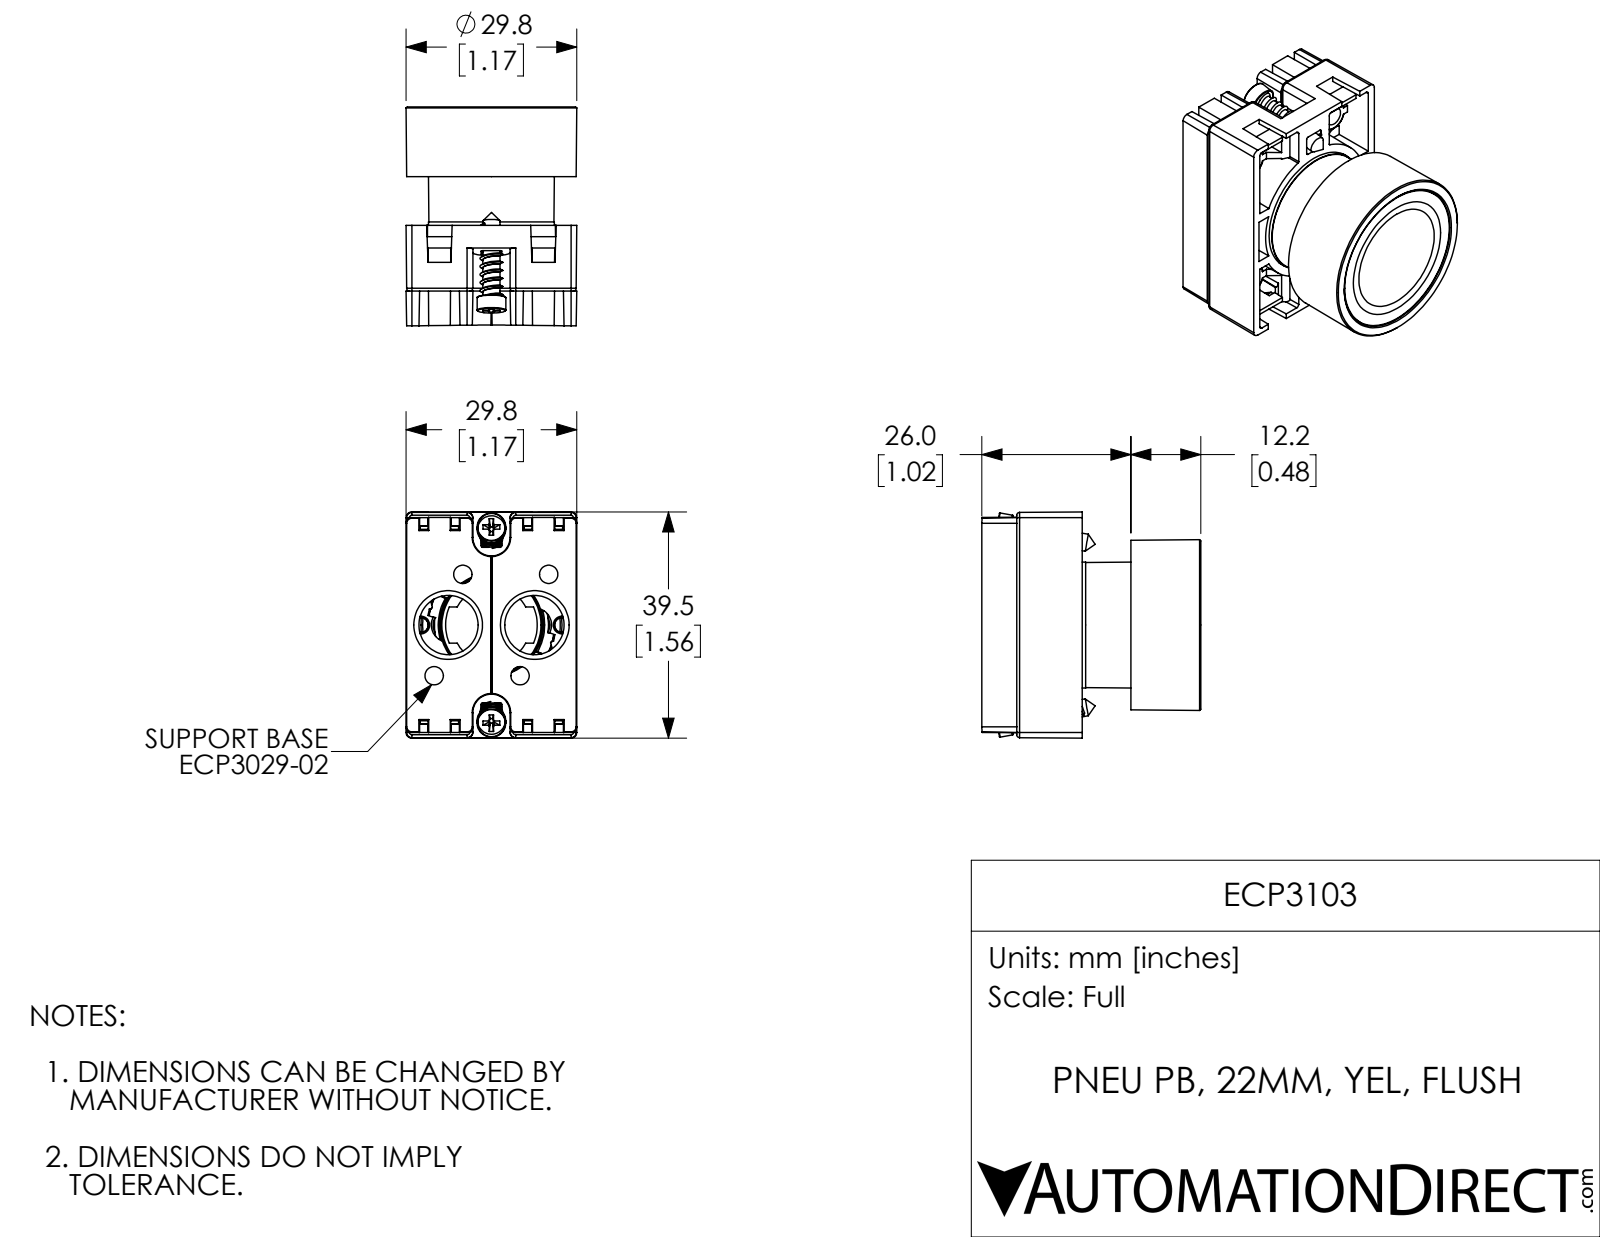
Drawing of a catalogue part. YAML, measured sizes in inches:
part_name: "ECP3103"
step_written_by: "SolidWorks 2017 (AUTOMOTIVE_DESIGN)"
units: inches
bodies: {solids: 7, faces: 778, planar: 363, cylindrical: 131, other: 284}
overall_size: [1.555, 1.505, 1.173]
volume: 0.893
surface_area: 29.03
round_holes:
  - {diameter: 0.081, count: 4}
  - {diameter: 0.407, count: 2}
  - {diameter: 0.697, count: 1}
  - {diameter: 0.732, count: 1}
round_bosses_or_shafts:
  - {diameter: 0.197, count: 2}
  - {diameter: 0.118, count: 2}
  - {diameter: 1.016, count: 1}
  - {diameter: 0.866, count: 1}
partial_cylinders:
  - {radius: 0.02, count: 18}
  - {radius: 0.006, count: 8}
  - {radius: 0.012, count: 8}
  - {radius: 0.008, count: 4}
  - {radius: 0.039, count: 4}
  - {radius: 0.008, count: 2}
  - {radius: 0.118, count: 2}
  - {radius: 0.128, count: 2}
face_to_face_distances: [1.195, 0.963, 0.177, 0.067, 0.715, 0.744, 0.451, 0.587, 0.519, 0.256]
hole_center_spacings: [0.304, 0.541, 0.817, 0.295, 0.472, 0.972, 1.081, 0.591]
